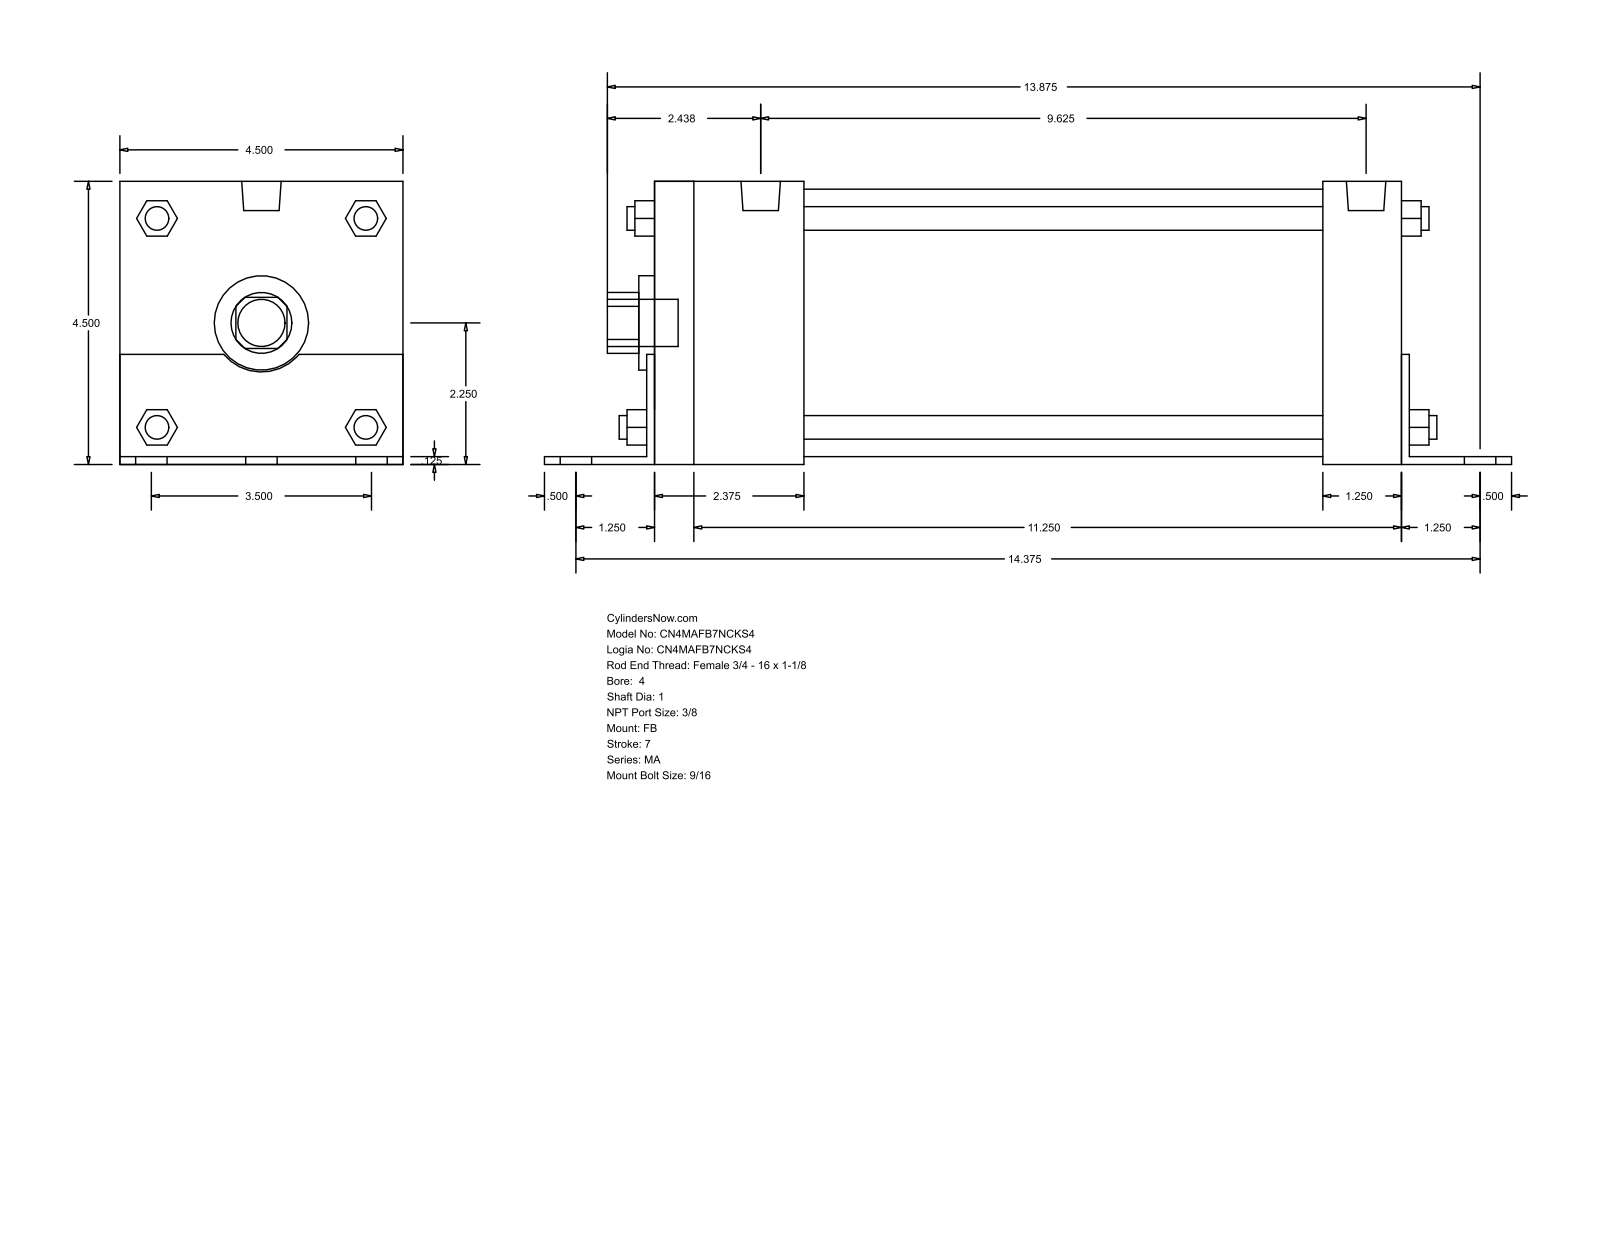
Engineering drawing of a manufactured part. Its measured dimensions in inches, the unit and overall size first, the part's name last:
Units: inches
Overall size (bounding box): 15.375 × 4.502 × 4.5
Round holes (diameter × count): ⌀1 ×1, ⌀1.5 ×1, ⌀4.25 ×1
Round bosses / shafts (diameter × count): ⌀0.563 ×6, ⌀0.437 ×4, ⌀0.375 ×4, ⌀0.627 ×2, ⌀0.75 ×1
Partial cylindrical surfaces — rounded edges, fillets, slot ends (radius × count): R0.484 ×1, R0.78 ×1
Main face-to-face distances: 4.5, 0.125, 4.502, 12, 0.123, 4.377, 11.875, 12.125, 10.75, 10.625
Bodies: 0 solids, 140 faces (105 planar, 35 cylindrical, 0 other)
Part name (STEP PRODUCT): MA_FB__0400_1
STEP written by: GSSL Pune (CONFIG_CONTROL_DESIGN)
